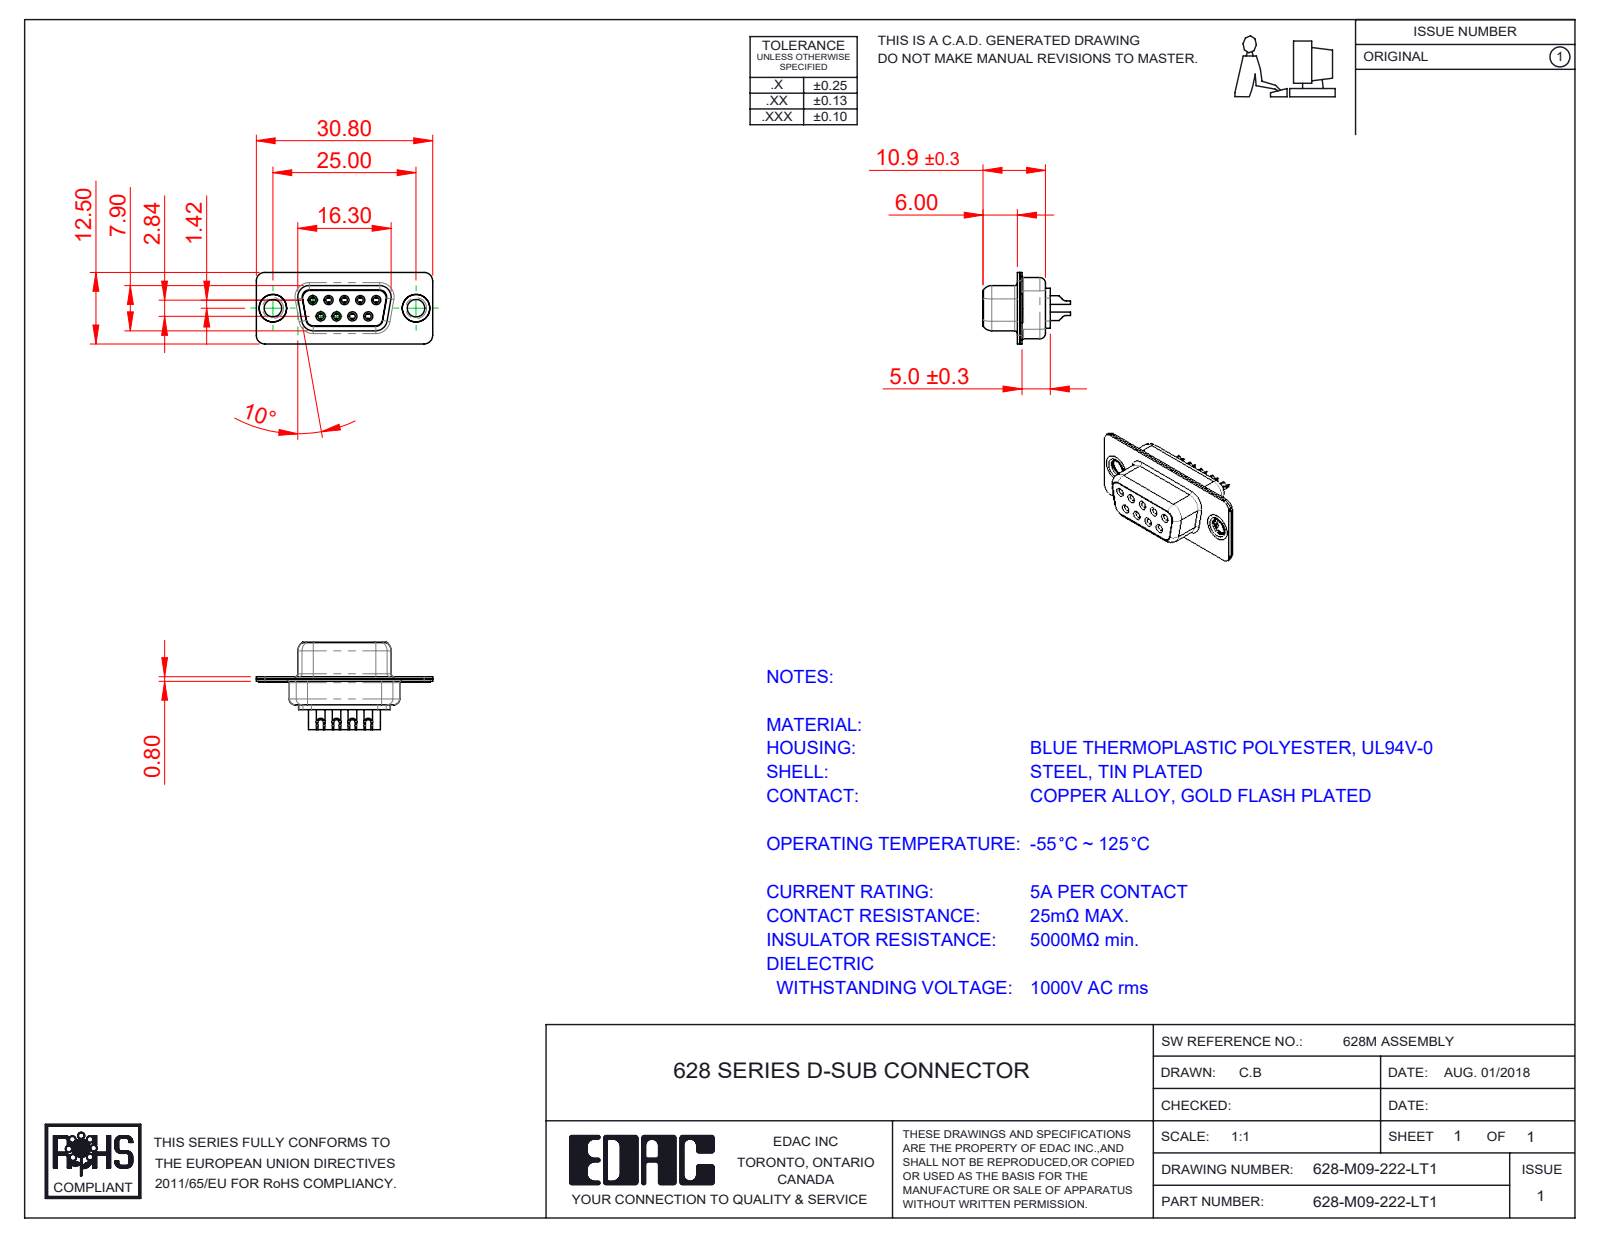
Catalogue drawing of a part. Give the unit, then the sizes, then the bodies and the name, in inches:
Units: inches
Overall size (bounding box): 1.213 × 0.6 × 0.492
Round holes (diameter × count): ⌀0.039 ×9, ⌀0.043 ×9, ⌀0.067 ×9, ⌀0.071 ×9, ⌀0.079 ×9, ⌀0.12 ×2, ⌀0.157 ×2, ⌀0.189 ×2
Round bosses / shafts (diameter × count): ⌀0.087 ×9, ⌀0.063 ×9, ⌀0.059 ×9, ⌀0.197 ×2, ⌀0.193 ×2, ⌀0.14 ×2
Partial cylindrical surfaces — rounded edges, fillets, slot ends (radius × count): R0.059 ×16, R0.079 ×12, R0.053 ×8, R0.063 ×8, R0.039 ×6, R0.01 ×4, R0.02 ×4, R0.024 ×4
Main face-to-face distances: 0.016, 0.055, 0.018, 0.333, 0.031, 0.35, 0.071, 0.278, 0.039, 0.033
Hole centre spacings: 0.124, 0.109, 0.218, 0.198, 0.198, 0.327, 0.28, 0.294
Volume: 0.1 in³ · Surface area: 6.75 in²
Bodies: 14 solids, 749 faces (221 planar, 310 cylindrical, 218 other)
Part name (STEP PRODUCT): 628M Shell Front_09 Contacts; 628M Contact Row 2_22; 628M Shell Rear_09 Contacts; 628M Contact Row 1_22 (+3 more)
STEP written by: SolidWorks 2020 (CONFIG_CONTROL_DESIGN)
